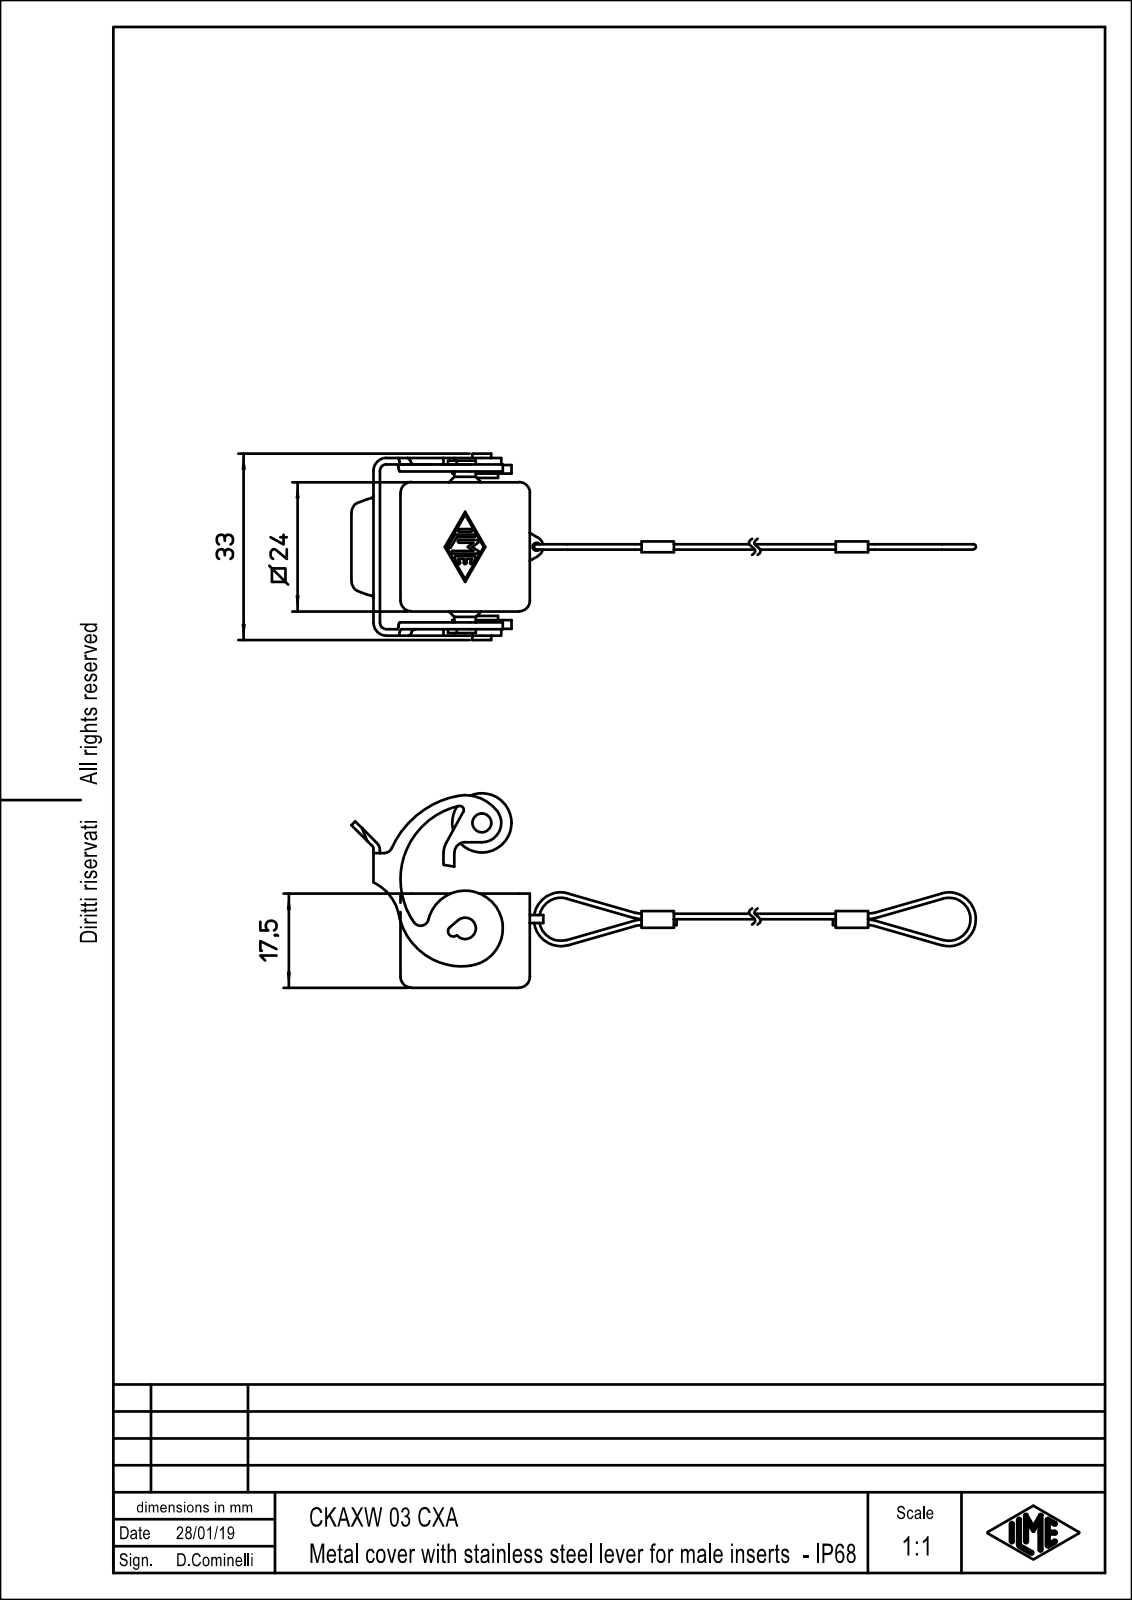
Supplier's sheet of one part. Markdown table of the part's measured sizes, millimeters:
| quantity | value |
| --- | --- |
| part name | CKAXW_03_CXA |
| STEP written by | PTC Creo Elements/Direct Modeling 19.0E 27-Jun-2016 (C) Parametric Technology GmbH (AUTOMOTIVE_DESIGN) |
| units | millimeters |
| bodies | 1 solid, 200 faces (72 planar, 104 cylindrical, 24 other) |
| overall size | 116 × 36.1 × 34.6 |
| volume | 4 905 mm³ |
| surface area | 7 361 mm² |
| round holes (diameter × count) | 1.5 × 1 |
| round bosses / shafts (diameter × count) | 1 × 6, 11 × 1, 6 × 1, 4 × 1, 3.5 × 1, 3.2 × 1 |
| partial cylindrical surfaces (radius × count) | 2 × 15, 1.2 × 10, 0.5 × 8, 1 × 4, 1.5 × 2, 2.4 × 2, 0.75 × 1, 3.6 × 1 |
| main face-to-face distances | 1.5, 22.5, 2, 1.2, 21, 24, 4.8, 25.8, 3.3, 27.3 |
